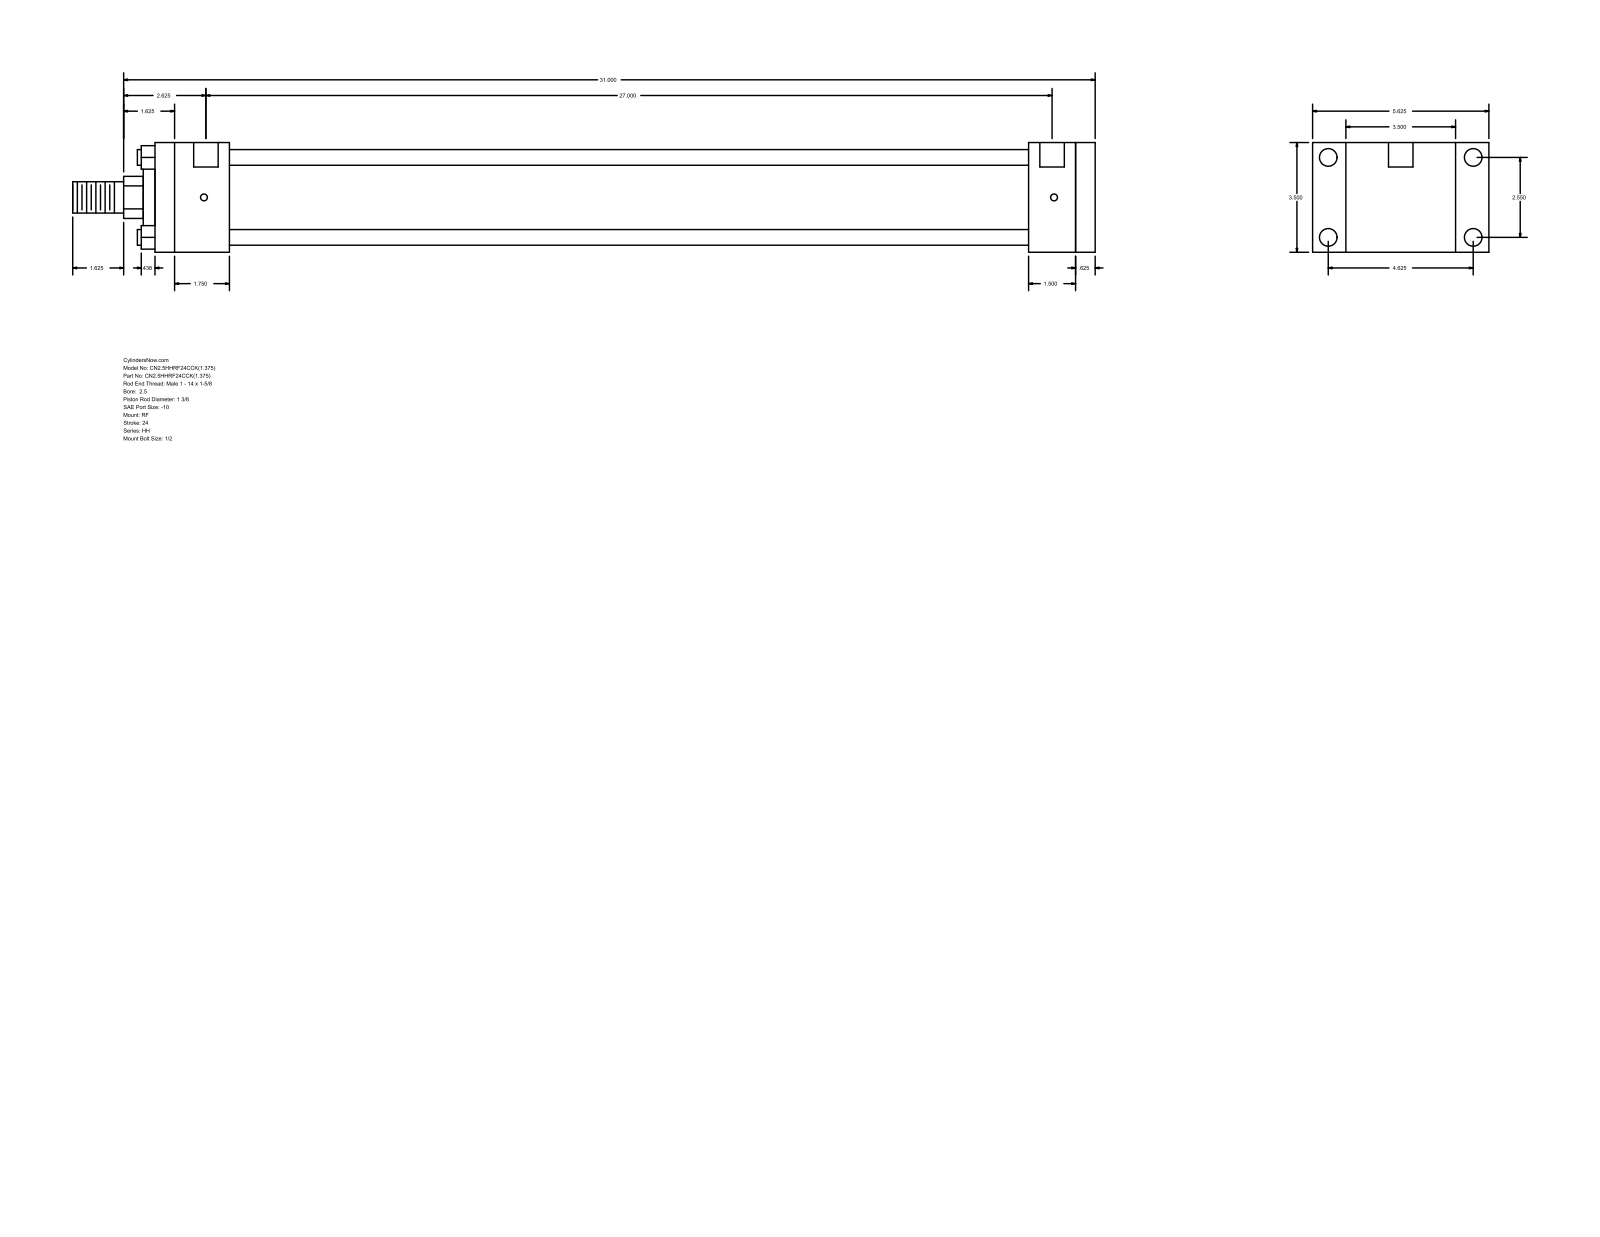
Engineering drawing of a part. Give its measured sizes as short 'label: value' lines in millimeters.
name: HH_RF__0250_1.375
written by: GSSL Pune (CONFIG_CONTROL_DESIGN)
unit: mm
bodies: 0 solids, 92 faces (64 planar, 28 cylindrical, 0 other)
size: 828.67 × 142.88 × 88.9
holes: 4× ⌀5.56, 4× ⌀14.3, 2× ⌀19.84
bosses: 4× ⌀12.7, 1× ⌀73.03, 1× ⌀50.8, 1× ⌀34.92, 1× ⌀25.4
rounds: 1× R17.06
face distances: 88.9, 762, 15.88, 746.12, 60.32, 685.8, 701.68, 708.02, 647.7, 38.1
hole spacings: 1.58, 64.76, 117.48, 134.15, 687.39, 688.97, 685.81
